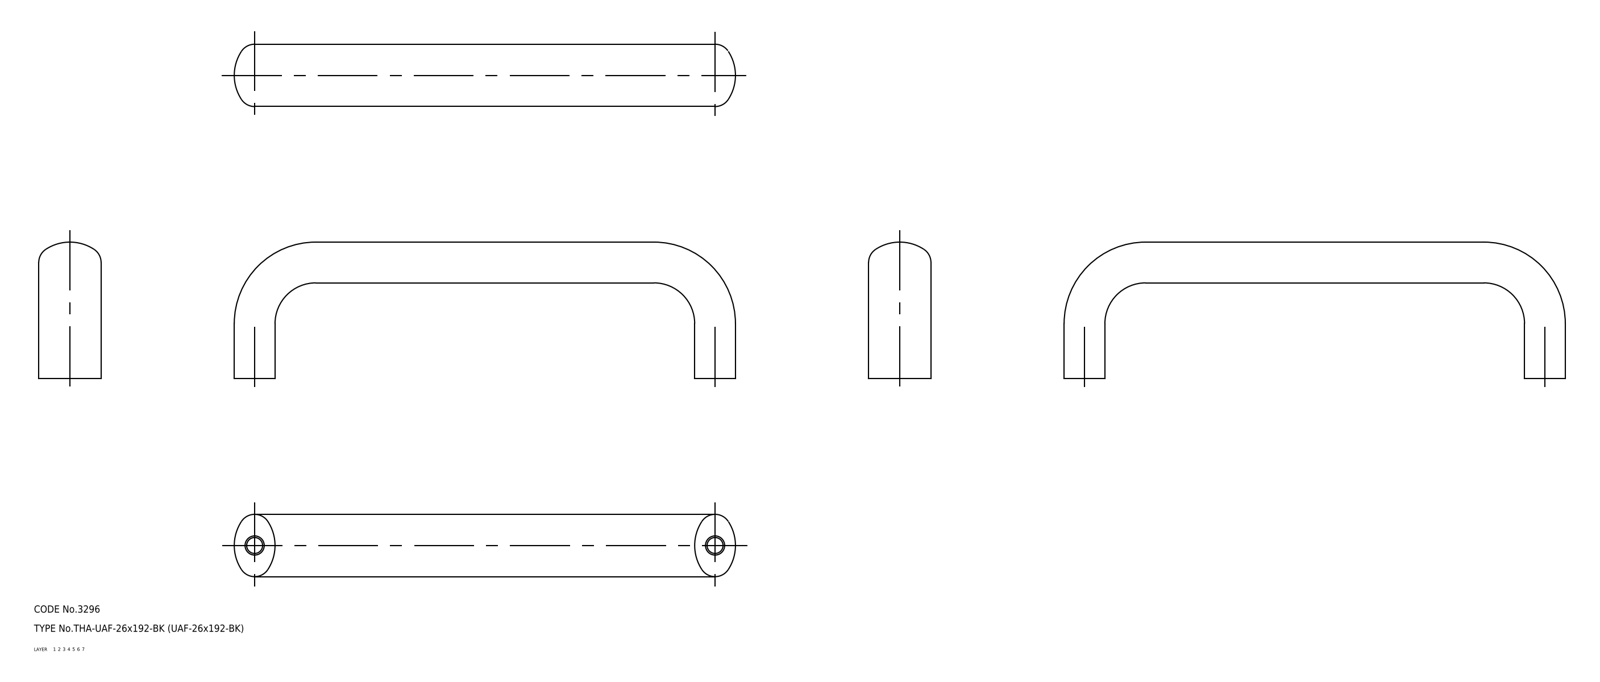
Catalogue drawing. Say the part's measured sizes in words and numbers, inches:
The part is named "pull". Its 3-D file was written by "CADfix (AUTOMOTIVE_DESIGN)". It is 1 solid with 18 faces: 0 planar, 0 cylindrical and 18 other. Overall it measures 8.228 by 2.244 by 1.024 inches. Its volume is 5.581 cubic inches and its surface area 30.28 square inches.
